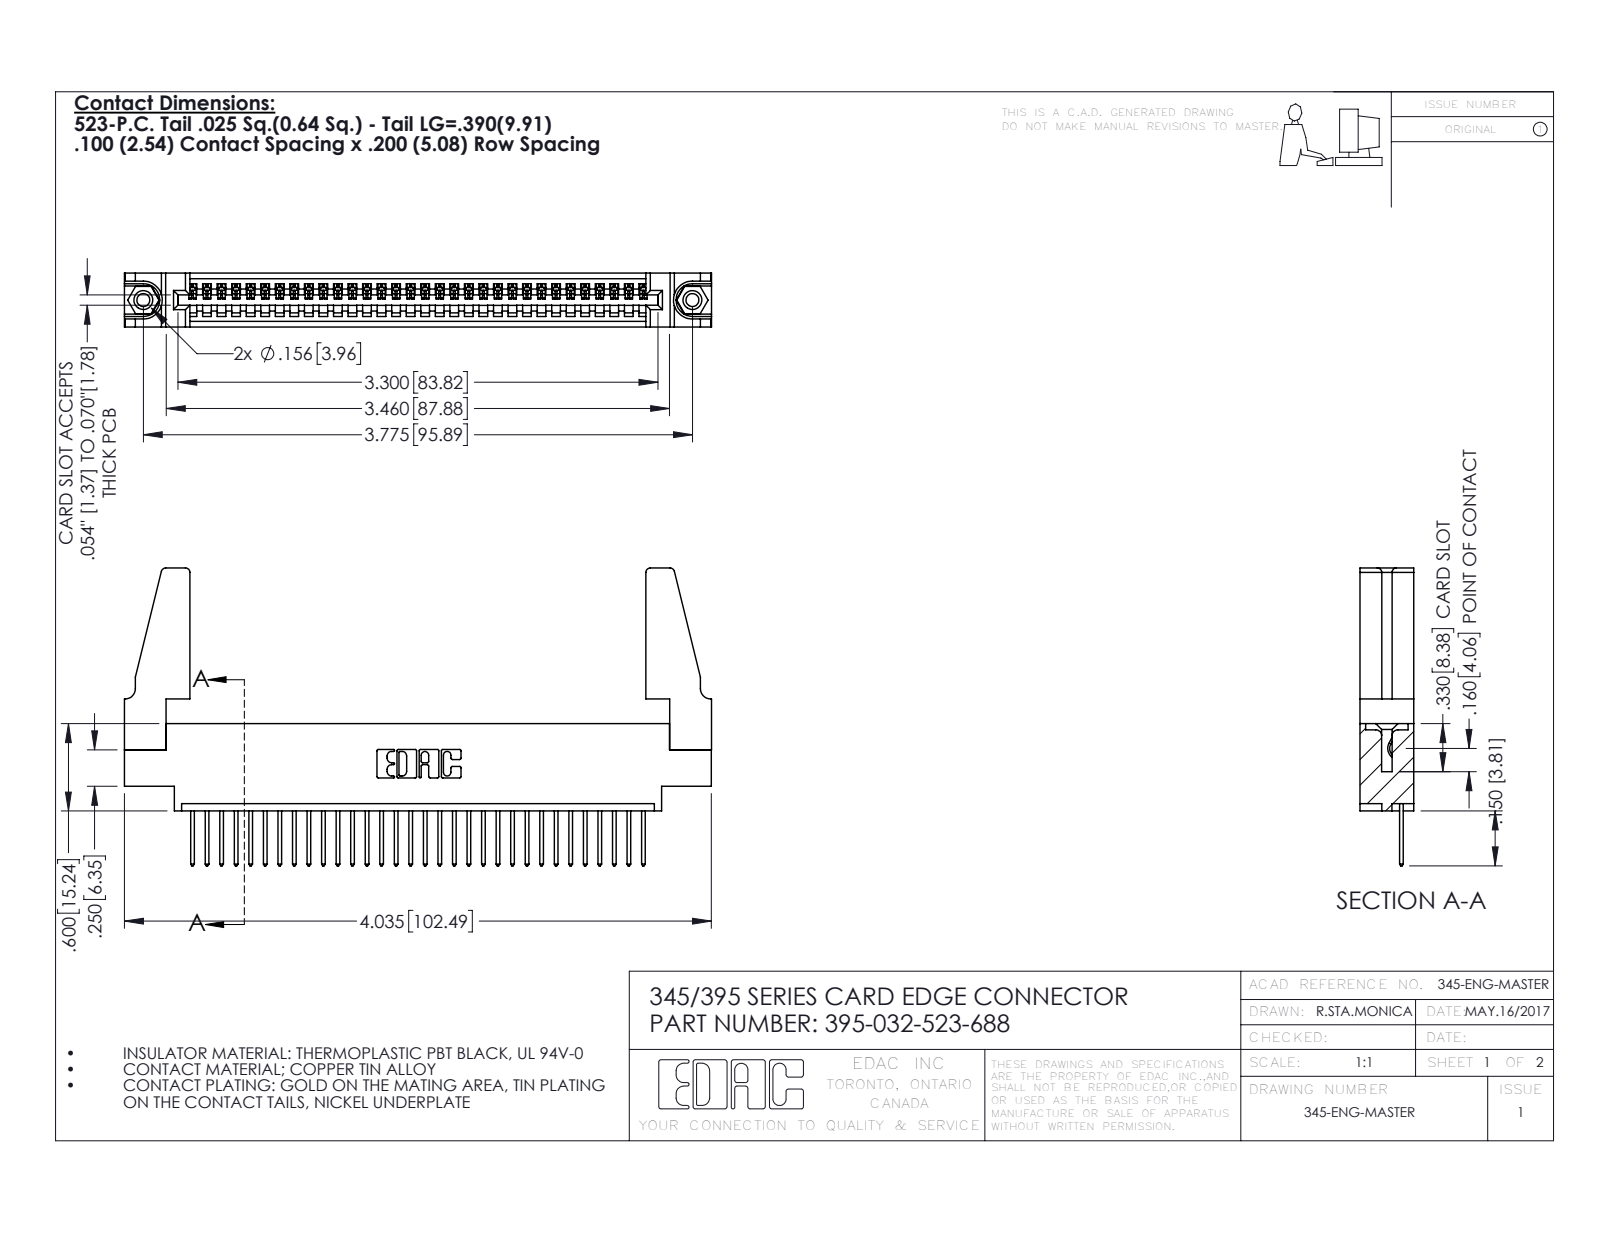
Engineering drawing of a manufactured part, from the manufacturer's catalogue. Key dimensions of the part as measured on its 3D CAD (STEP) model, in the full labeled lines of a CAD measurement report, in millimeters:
Part name (STEP PRODUCT): 345-292-001_345-293-123; 345 Part_0.170 Offset - 0.156 Dia-TH; 345-220-078_345-220-088; 395-032-523-688 (+1 more)
STEP written by: SolidWorks 2016 (CONFIG_CONTROL_DESIGN)
Units: millimetres
Bodies: 37 solids, 2110 faces (1436 planar, 658 cylindrical, 16 other)
Overall size (bounding box): 102.5 × 52 × 9.4
Volume: 12 800 mm³ · Surface area: 15 820 mm²
Round holes (diameter × count): ⌀2.3 ×2, ⌀3.2 ×2, ⌀4 ×2, ⌀1.6 ×1
Round bosses / shafts (diameter × count): ⌀3.9 ×2
Partial cylindrical surfaces — rounded edges, fillets, slot ends (radius × count): R0.2 ×64, R0.3 ×64, R0.3 ×22, R0.8 ×8, R0.2 ×6, R0.8 ×6, R0.7 ×3, R0.8 ×2
Main face-to-face distances: 1.8, 9.4, 7.6, 2.5, 6.9, 0.6, 5.1, 5.7, 4.4, 3.8
Hole centre spacings: 6.9, 89.9, 95.9
